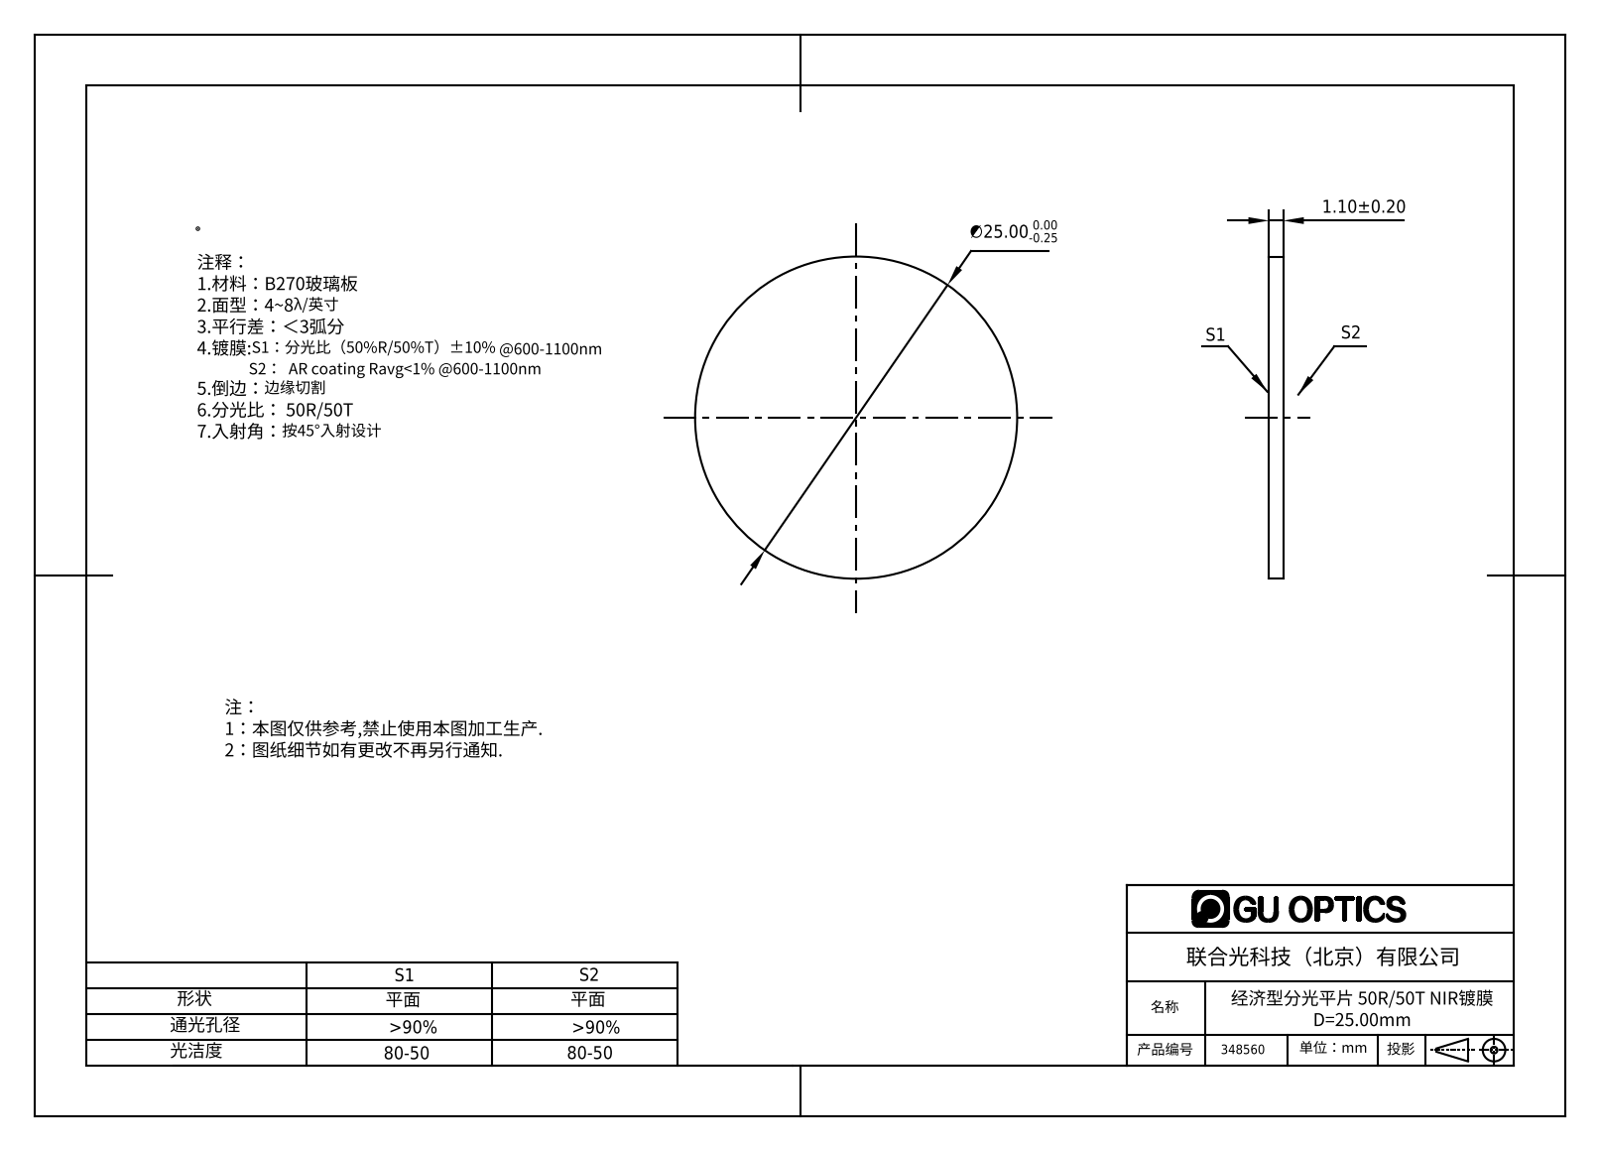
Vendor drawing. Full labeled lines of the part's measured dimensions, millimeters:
Part name (STEP PRODUCT): 348560
STEP written by: SolidWorks 2020 (CONFIG_CONTROL_DESIGN)
Units: millimetres
Bodies: 1 solid, 3 faces (2 planar, 1 cylindrical, 0 other)
Overall size (bounding box): 25 × 25 × 1.1
Volume: 540 mm³ · Surface area: 1 068 mm²
Round bosses / shafts (diameter × count): ⌀25 ×1
Main face-to-face distances: 1.1
